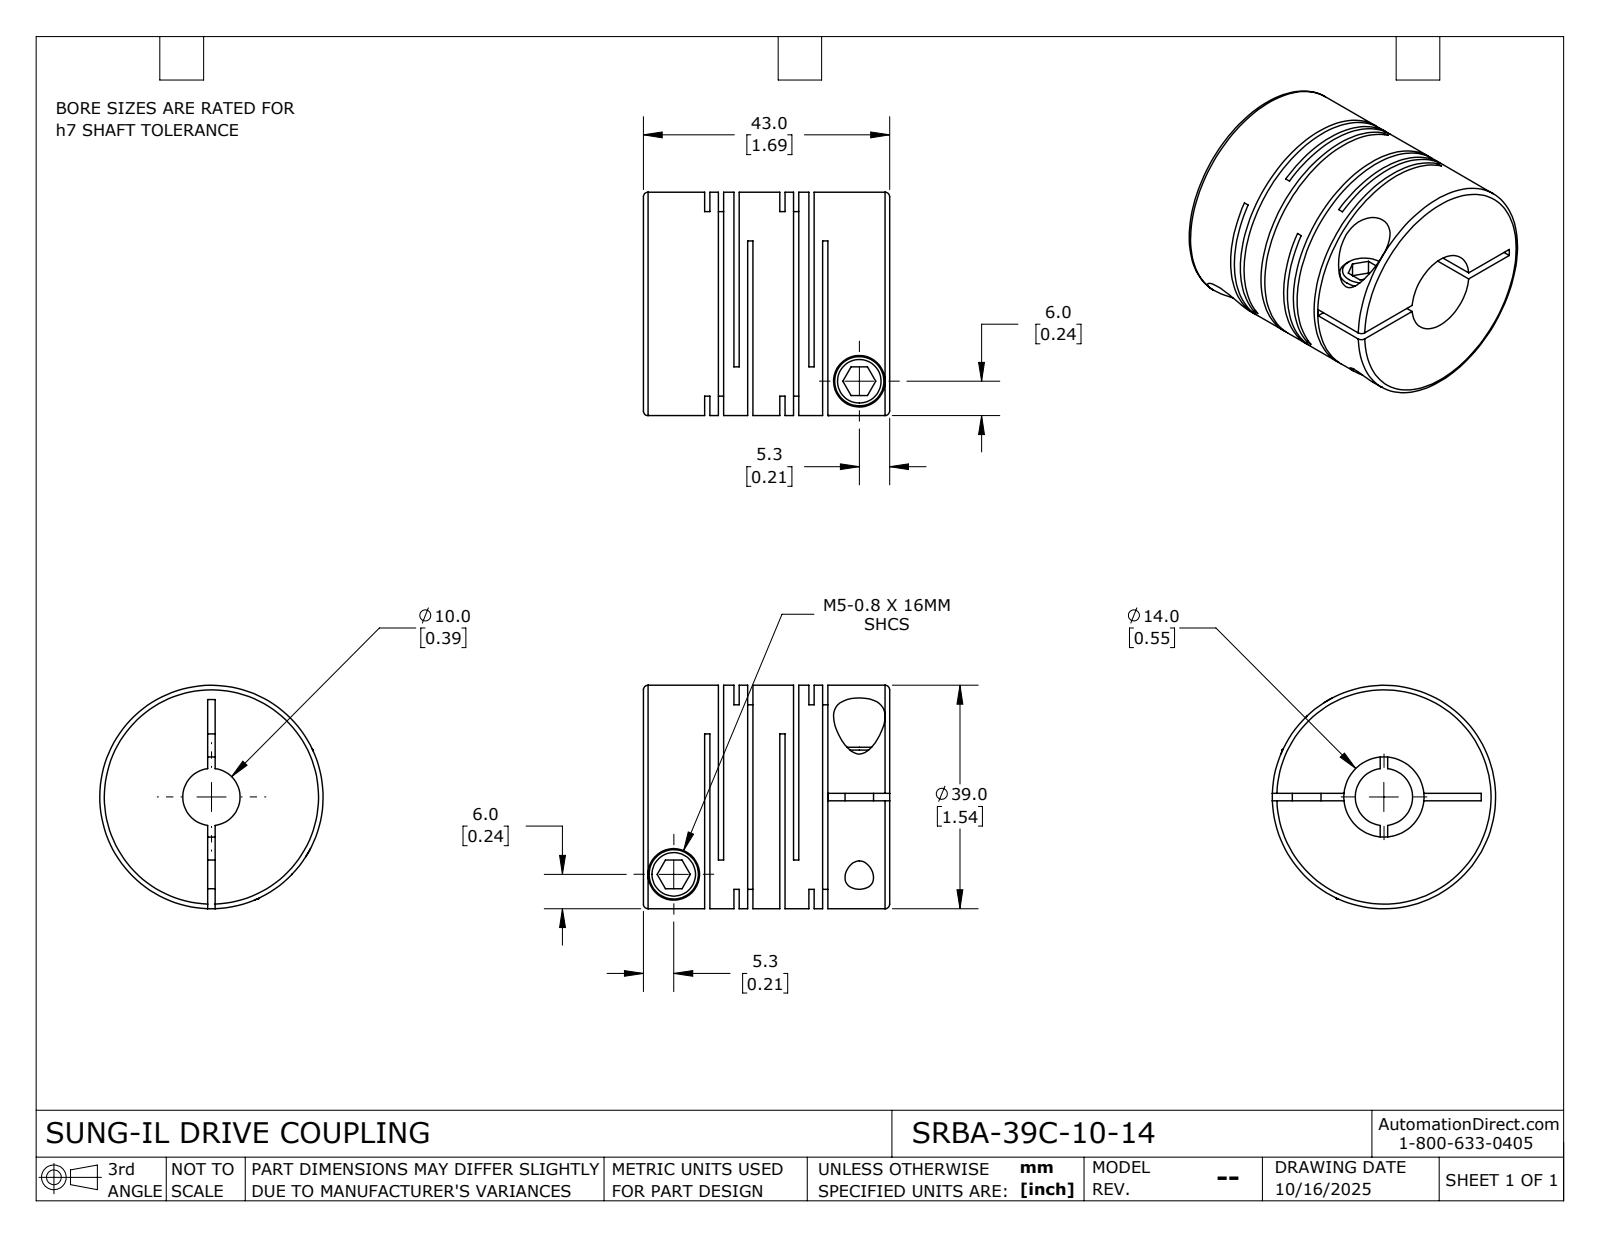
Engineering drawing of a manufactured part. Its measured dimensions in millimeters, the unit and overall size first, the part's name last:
Units: millimetres
Overall size (bounding box): 43 × 39 × 39
Round holes (diameter × count): ⌀5 ×2, ⌀9 ×2, ⌀10 ×1, ⌀14 ×1
Round bosses / shafts (diameter × count): ⌀8.6 ×2, ⌀39 ×1
Main face-to-face distances: 13.1, 0.92, 2.4, 5.1, 10.7, 14.02, 18.2, 12.18, 3.32, 7.5
Volume: 37 738 mm³ · Surface area: 23 744 mm²
Bodies: 1 solid, 115 faces (60 planar, 42 cylindrical, 13 other)
Part name (STEP PRODUCT): SRBA-39C-10-14
STEP written by: SolidWorks 2024 (CONFIG_CONTROL_DESIGN)
